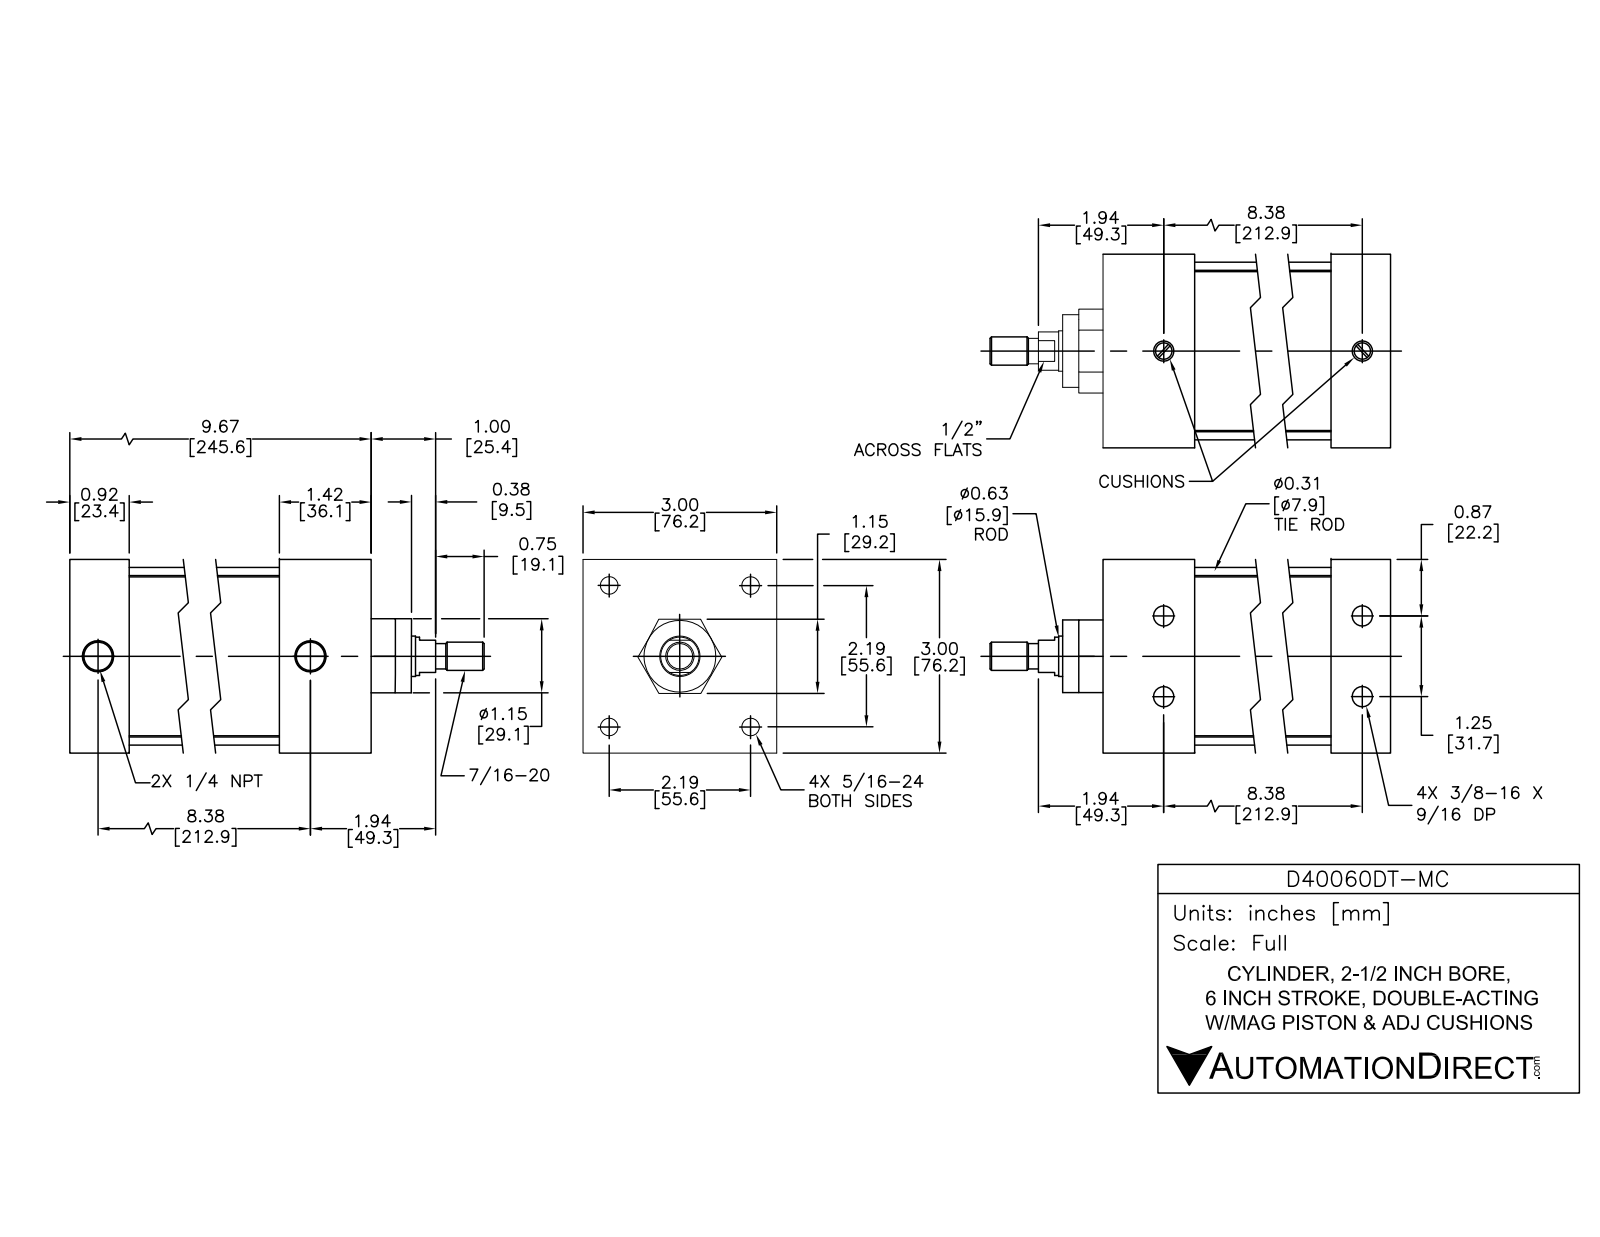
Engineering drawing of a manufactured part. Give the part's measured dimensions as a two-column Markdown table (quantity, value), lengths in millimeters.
| quantity | value |
| --- | --- |
| part name | D40060DT-MC; D40060DT-M PISTON; D40060DT-M BODY |
| STEP written by | SolidWorks 2015 (AUTOMOTIVE_DESIGN) |
| units | millimeters |
| bodies | 12 solids, 298 faces (94 planar, 114 cylindrical, 90 other) |
| overall size | 292 × 76.2 × 76.2 |
| volume | 634 500 mm³ |
| surface area | 183 600 mm² |
| round holes (diameter × count) | 6.8 × 4, 7.8 × 4, 9.1 × 4, 12.7 × 4, 7.5 × 2, 12.1 × 2, 15.9 × 1, 16 × 1, 63.5 × 1 |
| round bosses / shafts (diameter × count) | 12.3 × 4, 8 × 4, 7.2 × 4, 69.9 × 1, 63.4 × 1, 28.4 × 1, 15.8 × 1, 15 × 1 |
| partial cylindrical surfaces (radius × count) | 7.6 × 4 |
| main face-to-face distances | 76.2, 2, 186.1, 247.5, 221.6, 25.9, 36.1, 185.6, 211.5, 25.4 |
| hole center spacings | 39.5, 55.9, 213.2, 212.6, 15.9, 15.9, 31.8, 79 |
